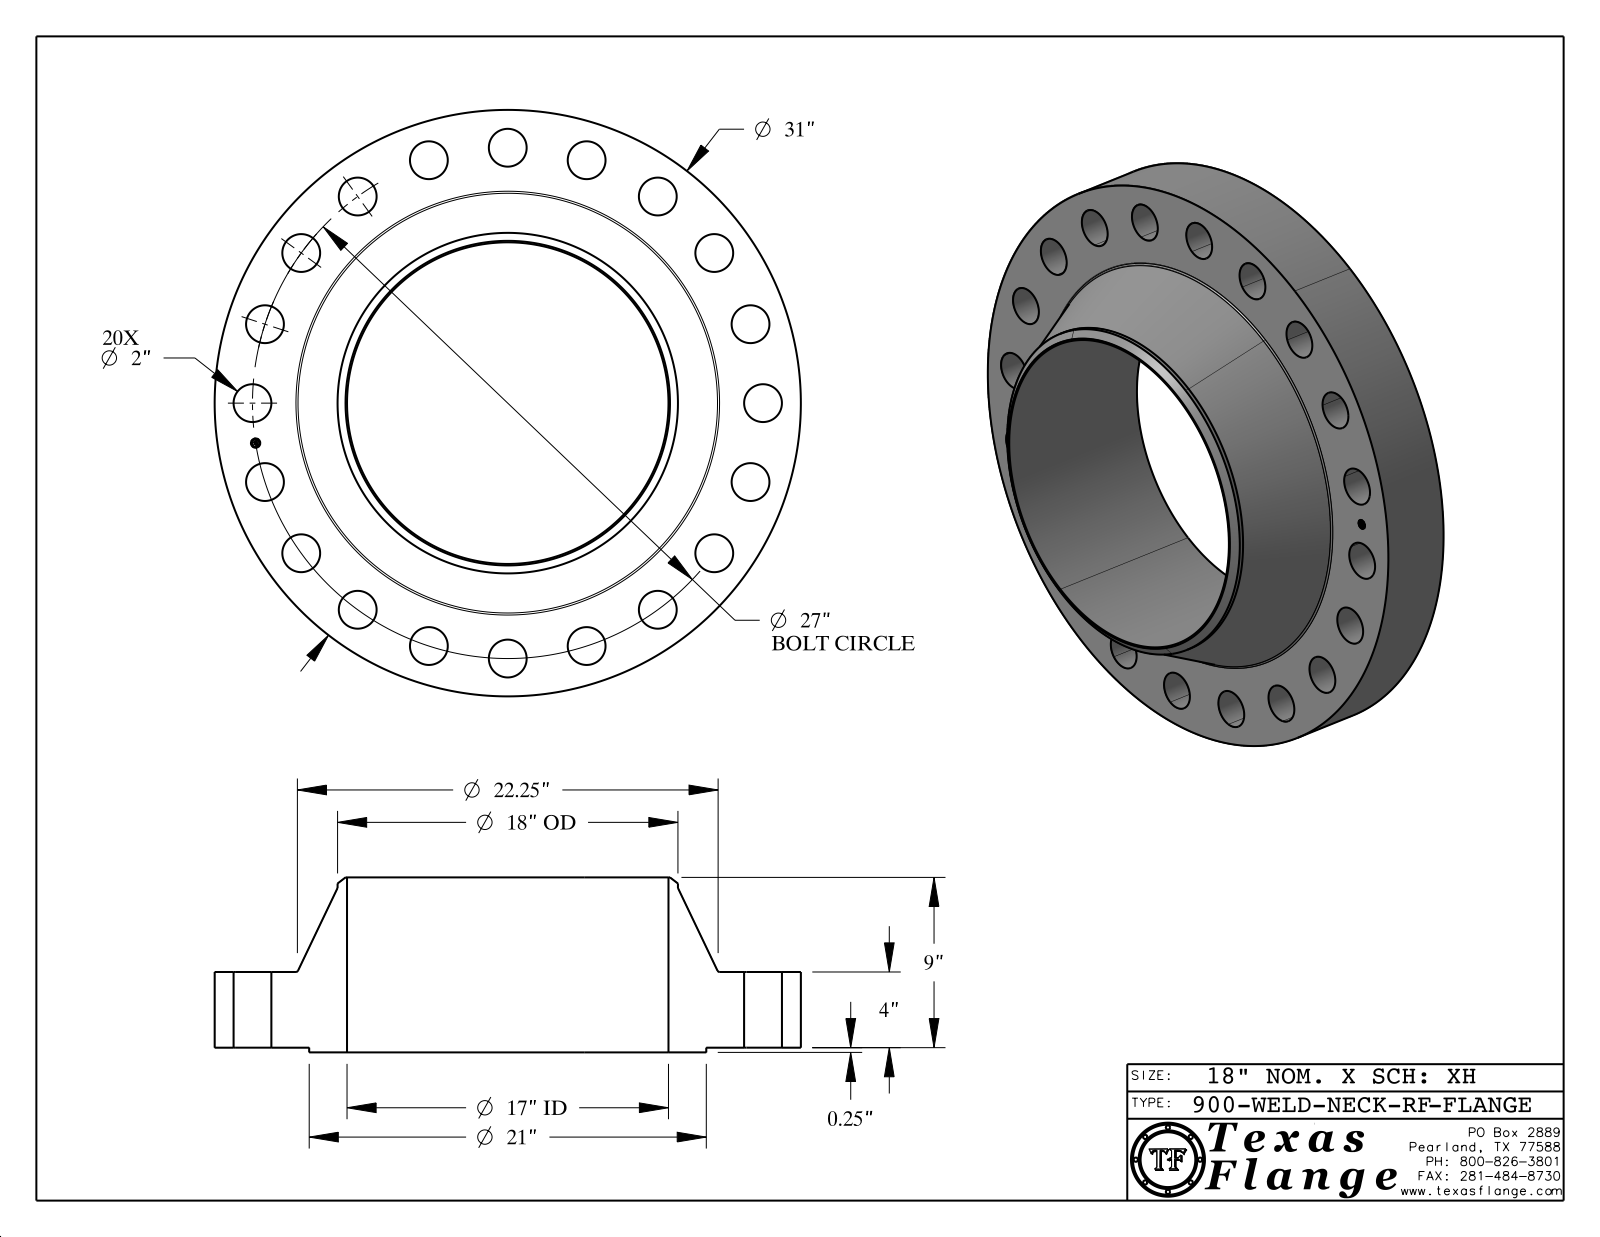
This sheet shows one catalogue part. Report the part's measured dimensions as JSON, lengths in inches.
{"part_name": "900-WELD-NECK-RF", "step_written_by": "CATIA V5 STEP AP214 (AUTOMOTIVE_DESIGN)", "units": "inches", "bodies": {"solids": 1, "faces": 443, "planar": 369, "cylindrical": 68, "other": 6}, "overall_size": [31, 31, 9.25], "volume_in3": 2311, "surface_area_in2": 2528, "round_holes": [[2, 20], [0.495, 1], [17, 1]], "round_bosses_or_shafts": [[0.03, 8], [31, 1], [21, 1], [18, 1], [0.39, 1]], "face_to_face_distances": [4, 0.25, 4.25, 9.25, 9, 5, 4.235, 3.985, 0.015, 5.015], "hole_center_spacings": [13.5, 21.843, 24.057, 25.678, 26.668, 4.224, 8.343, 12.258]}
